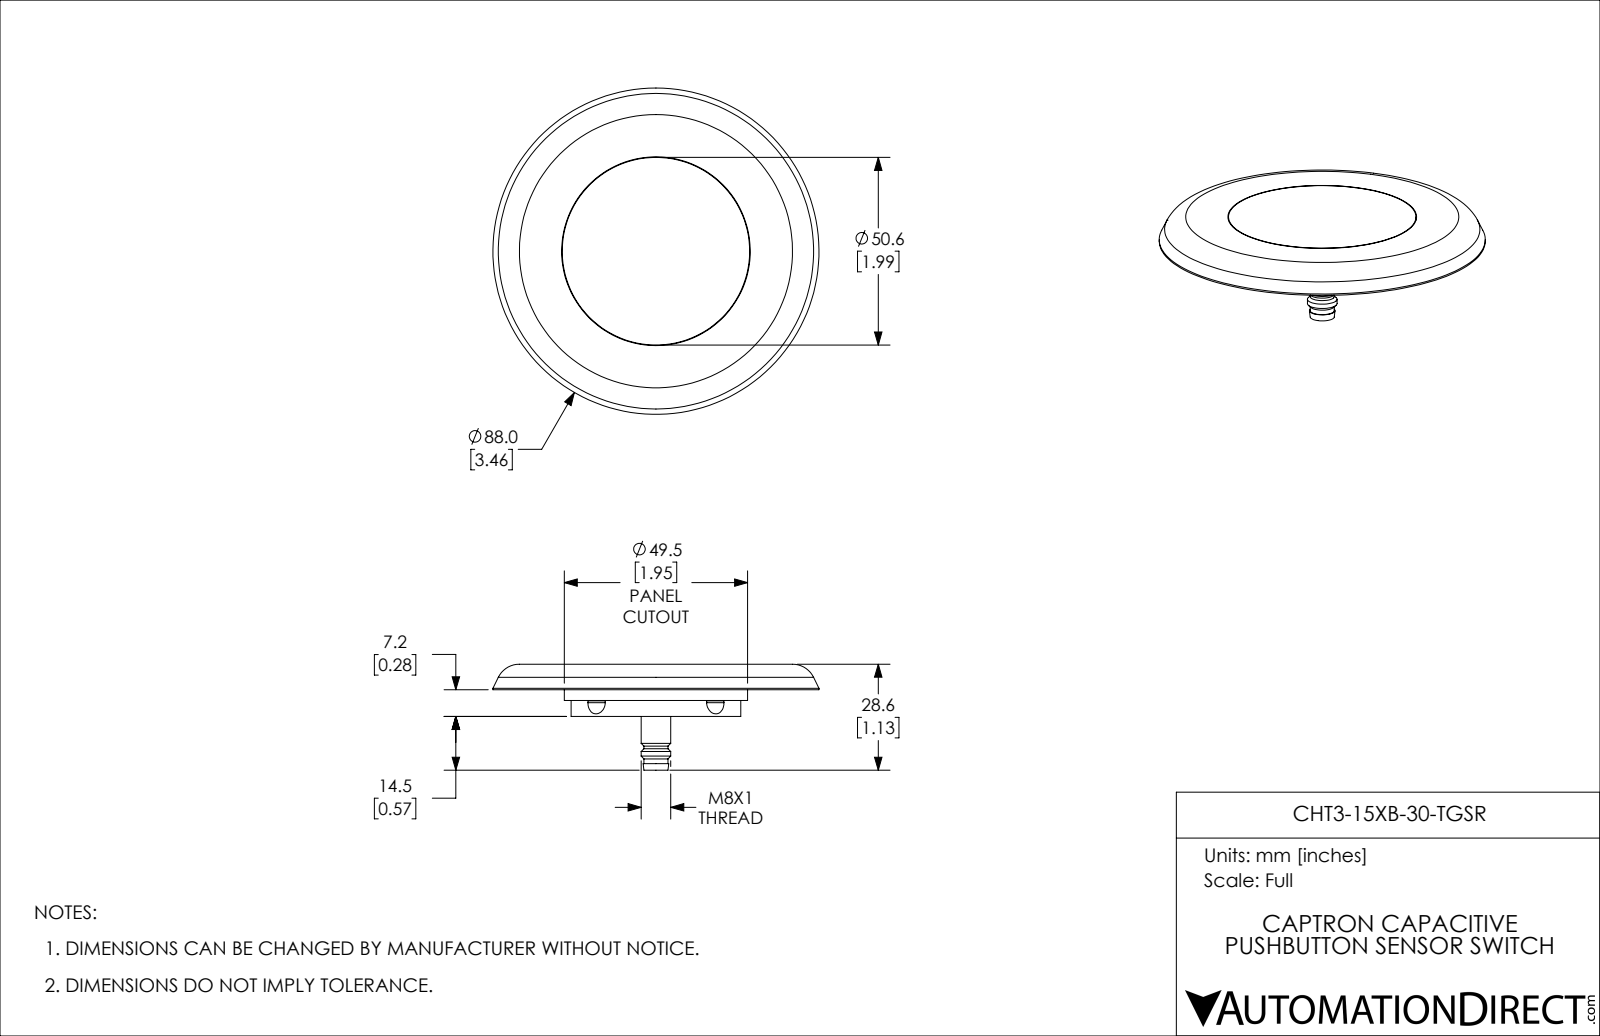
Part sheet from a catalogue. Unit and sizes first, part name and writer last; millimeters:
Units: millimetres
Overall size (bounding box): 88 × 88 × 28.6
Round holes (diameter × count): ⌀46.1 ×1, ⌀50.9 ×1
Round bosses / shafts (diameter × count): ⌀1 ×5, ⌀50.6 ×1, ⌀49.5 ×1, ⌀45.8 ×1, ⌀8 ×1, ⌀6.5 ×1
Partial cylindrical surfaces — rounded edges, fillets, slot ends (radius × count): R5 ×4, R0.5 ×2, R0.9 ×1, R1 ×1, R2.9 ×1
Main face-to-face distances: 6.9, 4.6, 2.3, 7.2, 11.8, 14.1, 0.5, 4.3, 7.7, 2.9
Volume: 49 980 mm³ · Surface area: 21 720 mm²
Bodies: 10 solids, 90 faces (25 planar, 40 cylindrical, 25 other)
Part name (STEP PRODUCT): CHT3-15XB-30-TGSR
STEP written by: SolidWorks 2019 (CONFIG_CONTROL_DESIGN)
